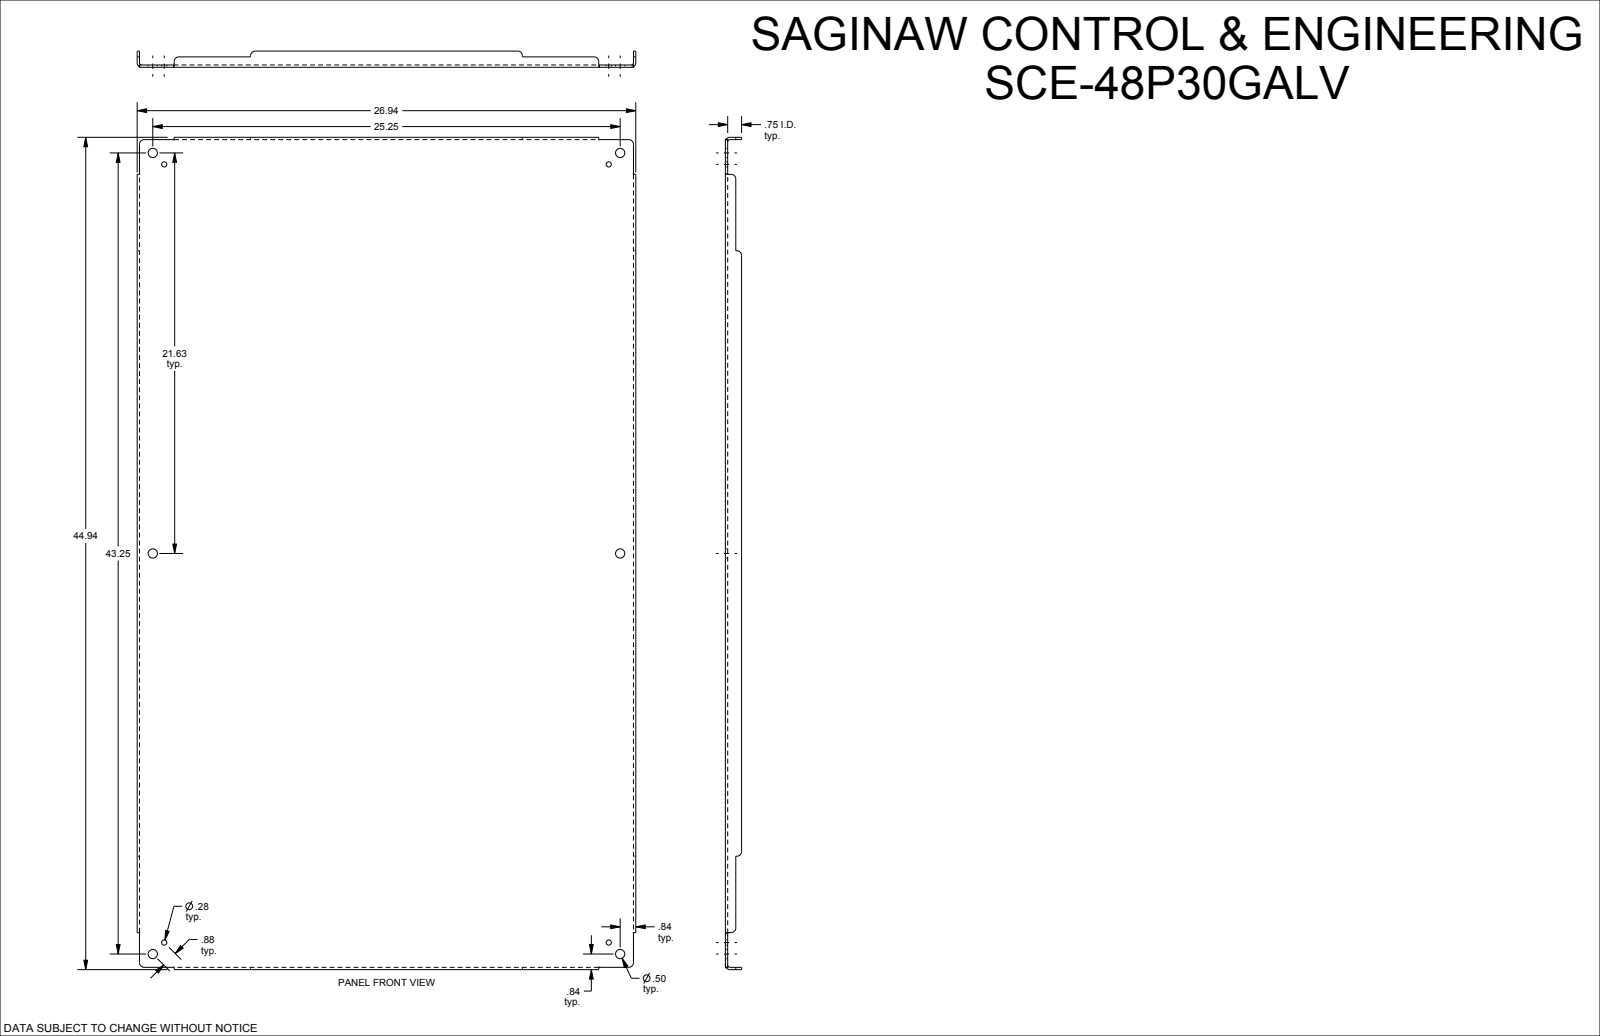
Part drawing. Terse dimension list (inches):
name: SCE-48P30GALV
written by: SolidWorks 2019 (CONFIG_CONTROL_DESIGN)
unit: in
bodies: 1 solid, 108 faces (46 planar, 38 cylindrical, 24 other)
size: 44.938 × 26.938 × 0.875
volume: 160.4 in³; area: 2 586 in²
holes: 6× ⌀0.5, 4× ⌀0.281
rounds: 12× R0.25, 4× R0.112, 4× R0.237
face distances: 0.125, 0.125, 26.813, 44.813, 26.687, 26.938, 44.687, 44.938, 0.75, 0.875
hole spacings: 0.875, 21.015, 21.625, 24.639, 32.372, 33.244, 42.635, 49.235
